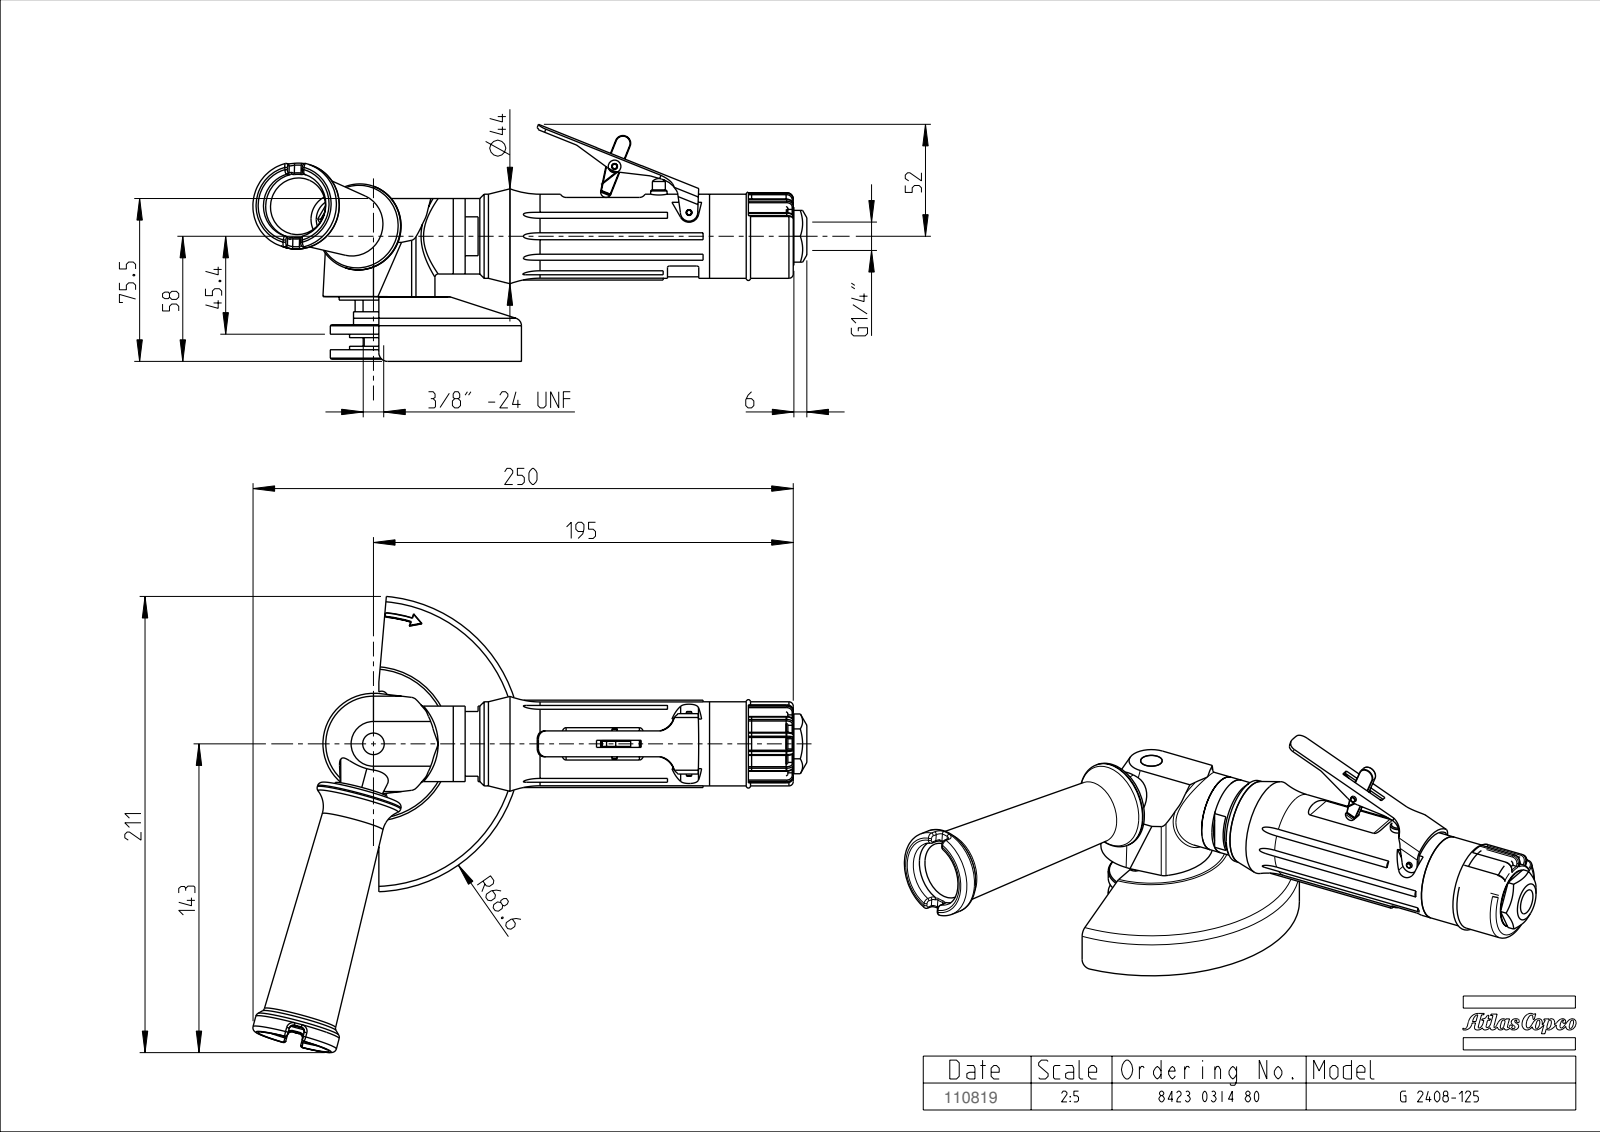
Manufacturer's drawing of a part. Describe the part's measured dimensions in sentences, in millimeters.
The part is named "TMP154320_SW". Its 3-D file was written by "PRO/ENGINEER BY PARAMETRIC TECHNOLOGY CORPORATION, 2008310 (CONFIG_CONTROL_DESIGN)". It is 0 solids with 423 faces: 118 planar, 172 cylindrical and 133 other. Overall it measures 256.8 by 211.48 by 109.9 millimeters. Round holes: 2 of diameter 6.2, 2 of diameter 7.2, 1 of diameter 4.2, 1 of diameter 8.43, 1 of diameter 11.5, 1 of diameter 26, 1 of diameter 30. Round bosses or shafts: 2 of diameter 40, 1 of diameter 39, 1 of diameter 38, 1 of diameter 35, 1 of diameter 25, 1 of diameter 22.15, 1 of diameter 18.5, 1 of diameter 17. Partial cylindrical surfaces (rounded edges, fillets, slot ends): 16 of radius 1, 15 of radius 0.5, 11 of radius 2, 7 of radius 0.3, 6 of radius 4, 5 of radius 0.7, 3 of radius 0.17, 2 of radius 3. The main face-to-face distances are 1.6, 6, 16, 4.4, 11.6, 29, 23, 13, 27.4, 11.4. The hole center spacings are 15, 2, 13, 28, 30.
